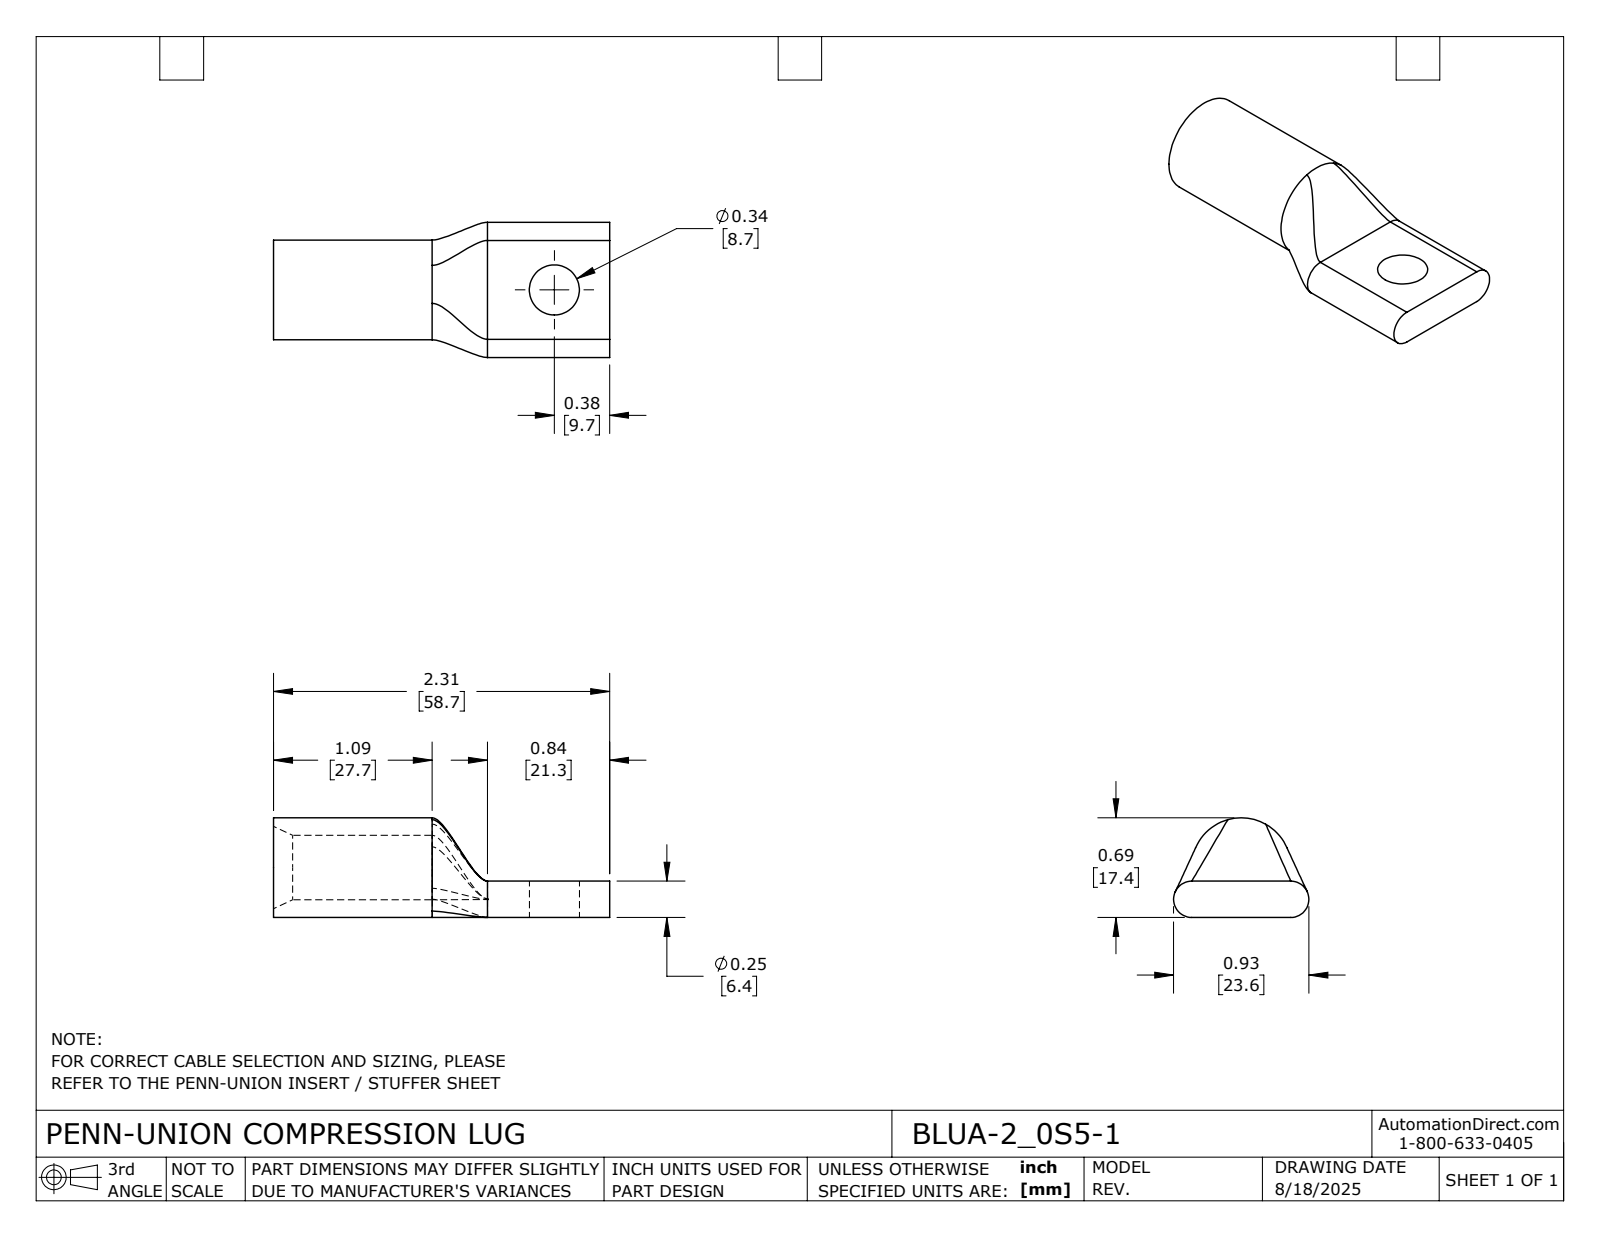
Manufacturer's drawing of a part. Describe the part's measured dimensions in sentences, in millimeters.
The part is named "BLUA-2_0S5-1". Its 3-D file was written by "SolidWorks 2024 (CONFIG_CONTROL_DESIGN)". It is 1 solid with 24 faces: 5 planar, 9 cylindrical and 10 other. Overall it measures 58.7 by 23.6 by 17.4 millimeters. Its volume is 7 700 cubic millimeters and its surface area 4 966 square millimeters. Round holes: 1 of diameter 8.7, 1 of diameter 11.3. Round bosses or shafts: 1 of diameter 17.4. Partial cylindrical surfaces (rounded edges, fillets, slot ends): 2 of radius 3.2. The main face-to-face distances are 6.4, 58.7, 37.3, 21.3.
